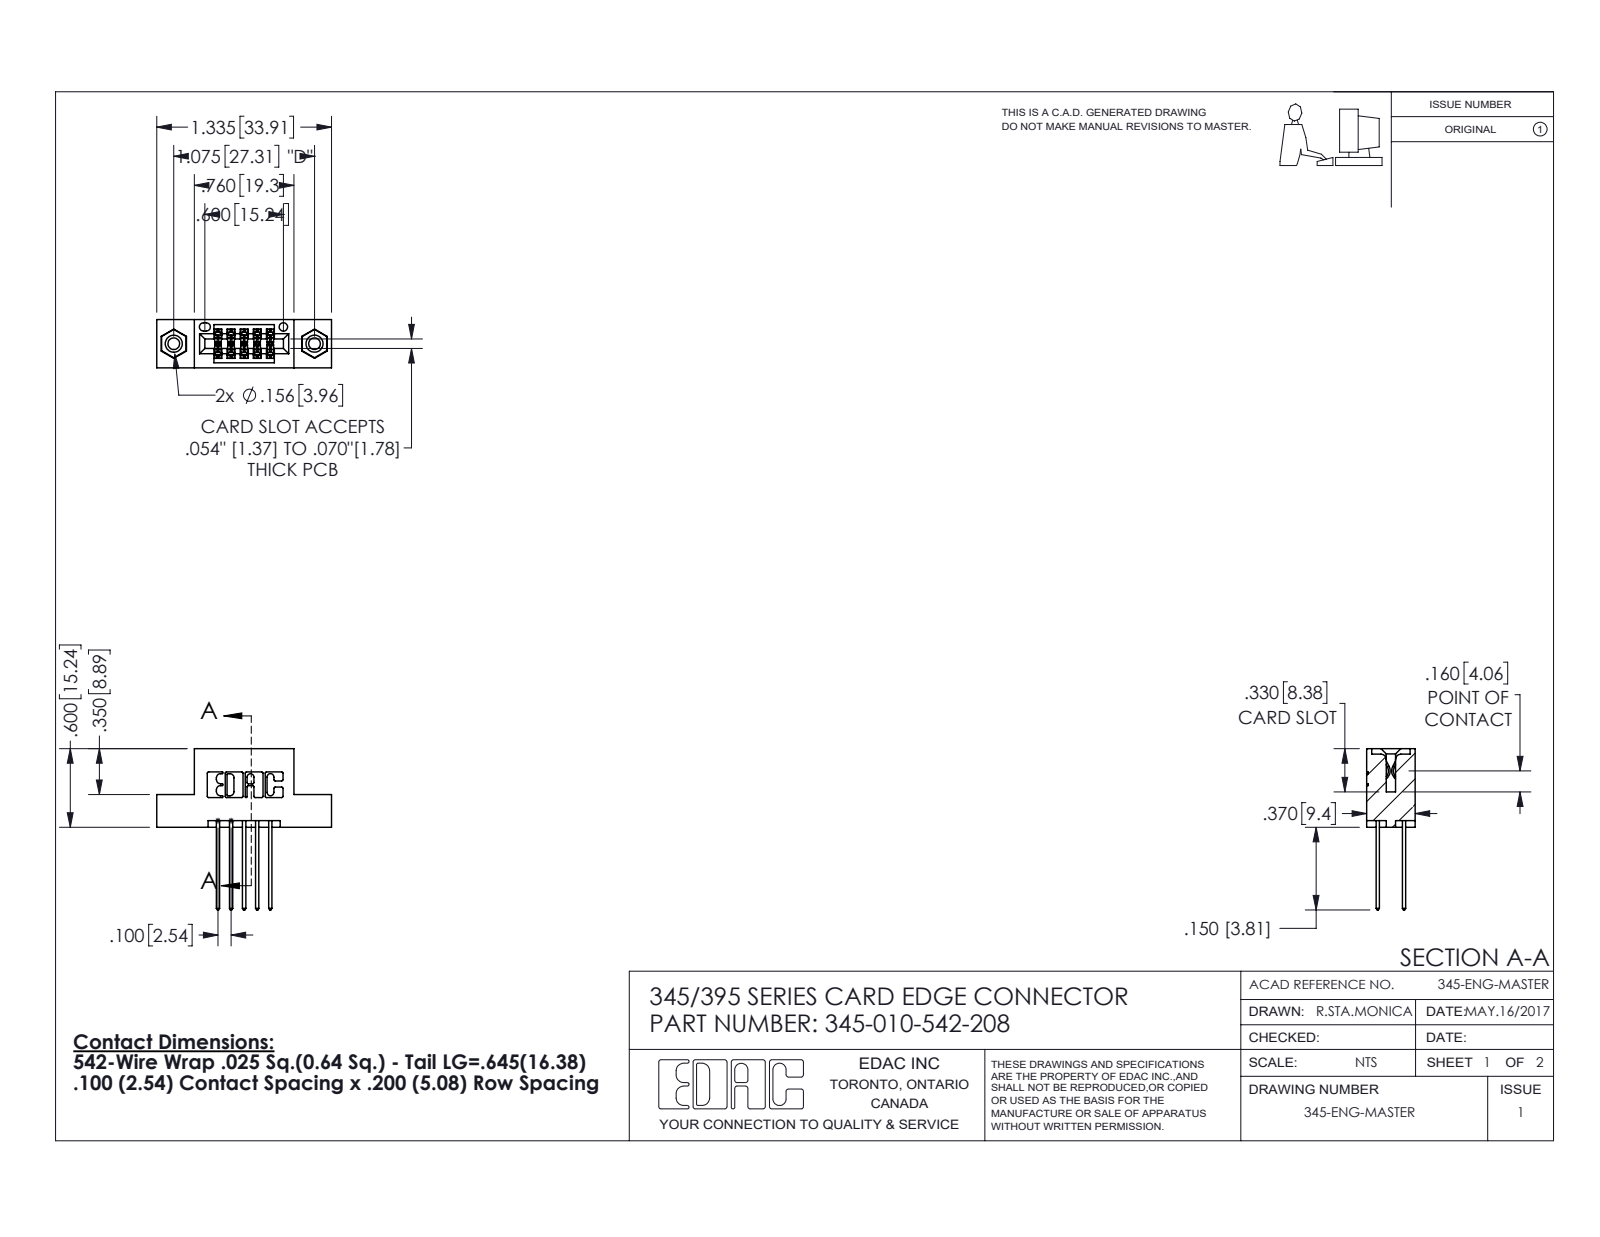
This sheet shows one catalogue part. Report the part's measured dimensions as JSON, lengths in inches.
{"part_name": "345-010-542-208; 345-250-001_345-250-003-102; 345 Part_Flush Mounting Lugs - 0.156 Dia-TI; 345-292-001_345-293-142", "step_written_by": "SolidWorks 2016 (CONFIG_CONTROL_DESIGN)", "units": "inches", "bodies": {"solids": 13, "faces": 686, "planar": 442, "cylindrical": 228, "other": 16}, "overall_size": [1.335, 1.232, 0.37], "volume_in3": 0.182, "surface_area_in2": 6.1, "round_holes": [[0.089, 2], [0.125, 2], [0.156, 2], [0.064, 1]], "round_bosses_or_shafts": [[0.155, 2]], "partial_cylinders_radius": [[0.01, 22], [0.006, 15], [0.01, 10], [0.007, 6], [0.031, 6], [0.026, 3], [0.014, 2], [0.019, 2]], "face_to_face_distances": [0.2, 0.072, 0.298, 0.1, 0.37, 0.098, 0.272, 0.025, 0.225, 0.35], "hole_center_spacings": [0.27, 0.847, 1.075]}
